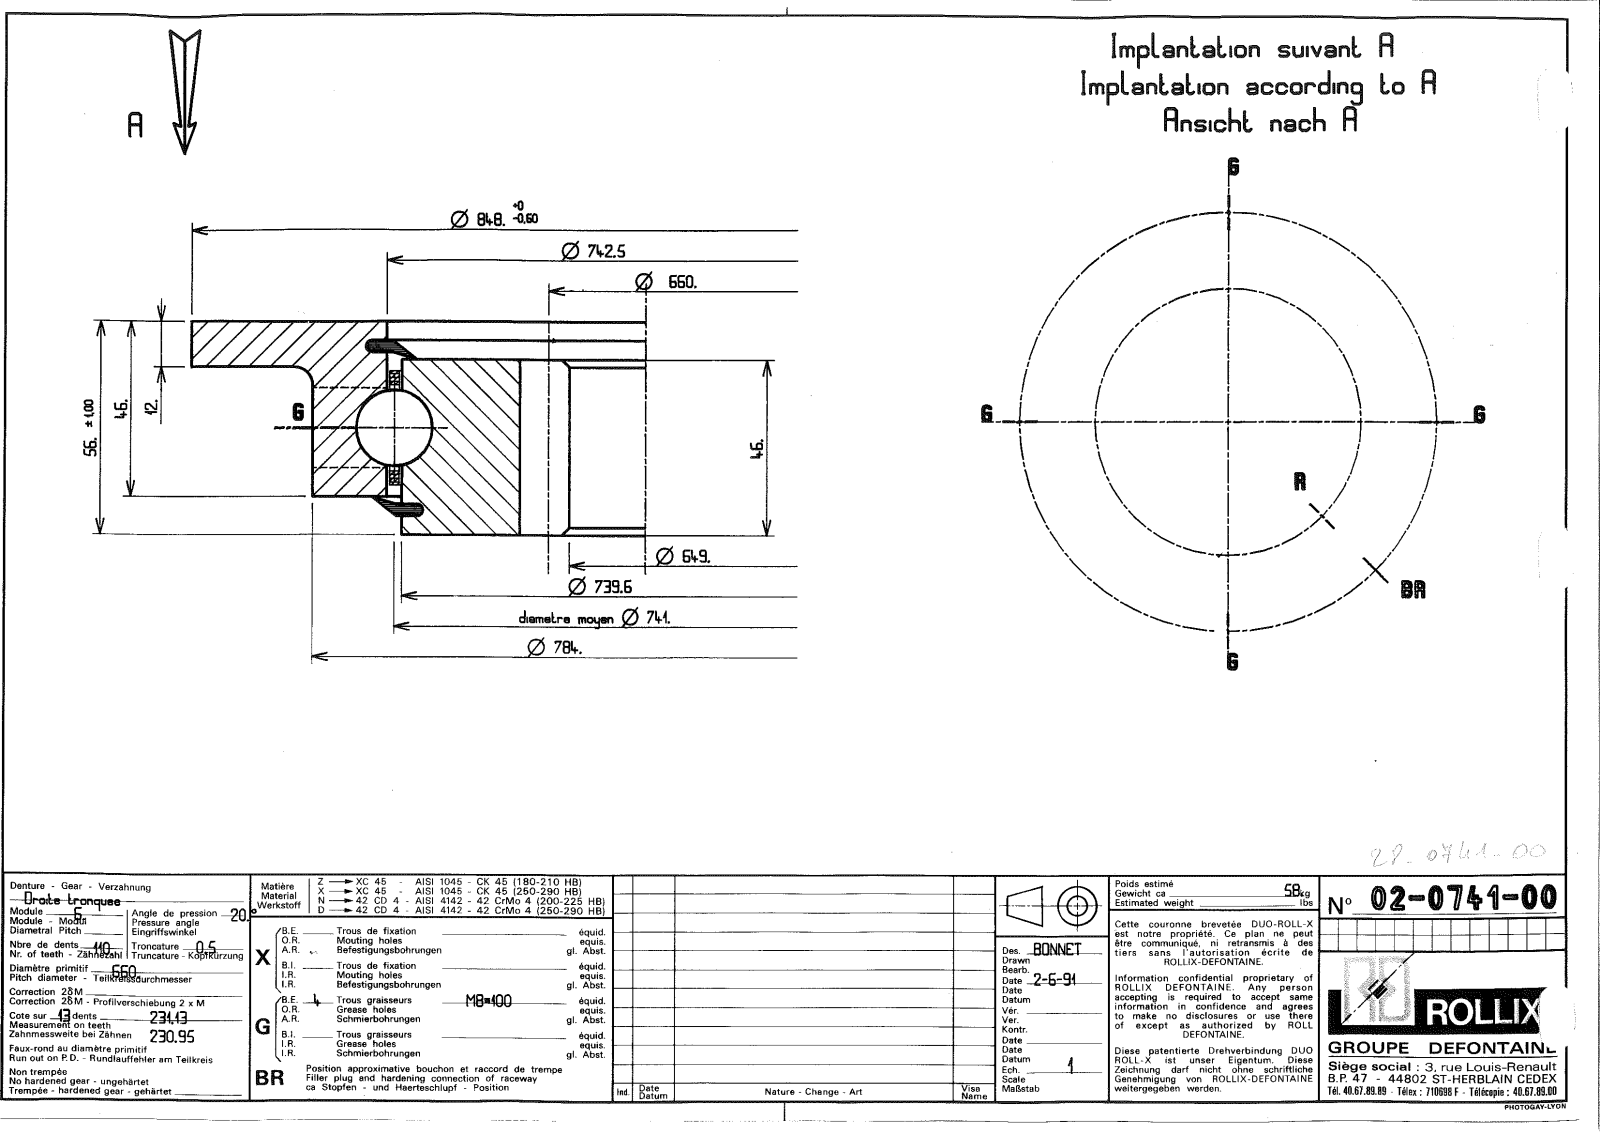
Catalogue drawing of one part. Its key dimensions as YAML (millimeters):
part_name: "22-0741-00"
step_written_by: "SolidWorks 2016 (CONFIG_CONTROL_DESIGN)"
units: millimeters
bodies: {solids: 9, faces: 816, planar: 273, cylindrical: 253, other: 290}
overall_size: [848, 848, 56]
volume: 6515000
surface_area: 1148000
round_holes:
  - {diameter: 7, count: 4}
  - {diameter: 745.5, count: 1}
round_bosses_or_shafts:
  - {diameter: 8, count: 4}
  - {diameter: 848, count: 1}
  - {diameter: 784, count: 1}
  - {diameter: 736.5, count: 1}
partial_cylinders:
  - {radius: 324.5, count: 1}
  - {radius: 337.5, count: 1}
face_to_face_distances: [10, 46, 56, 44, 2, 12, 34, 36, 4.95, 51.05]
